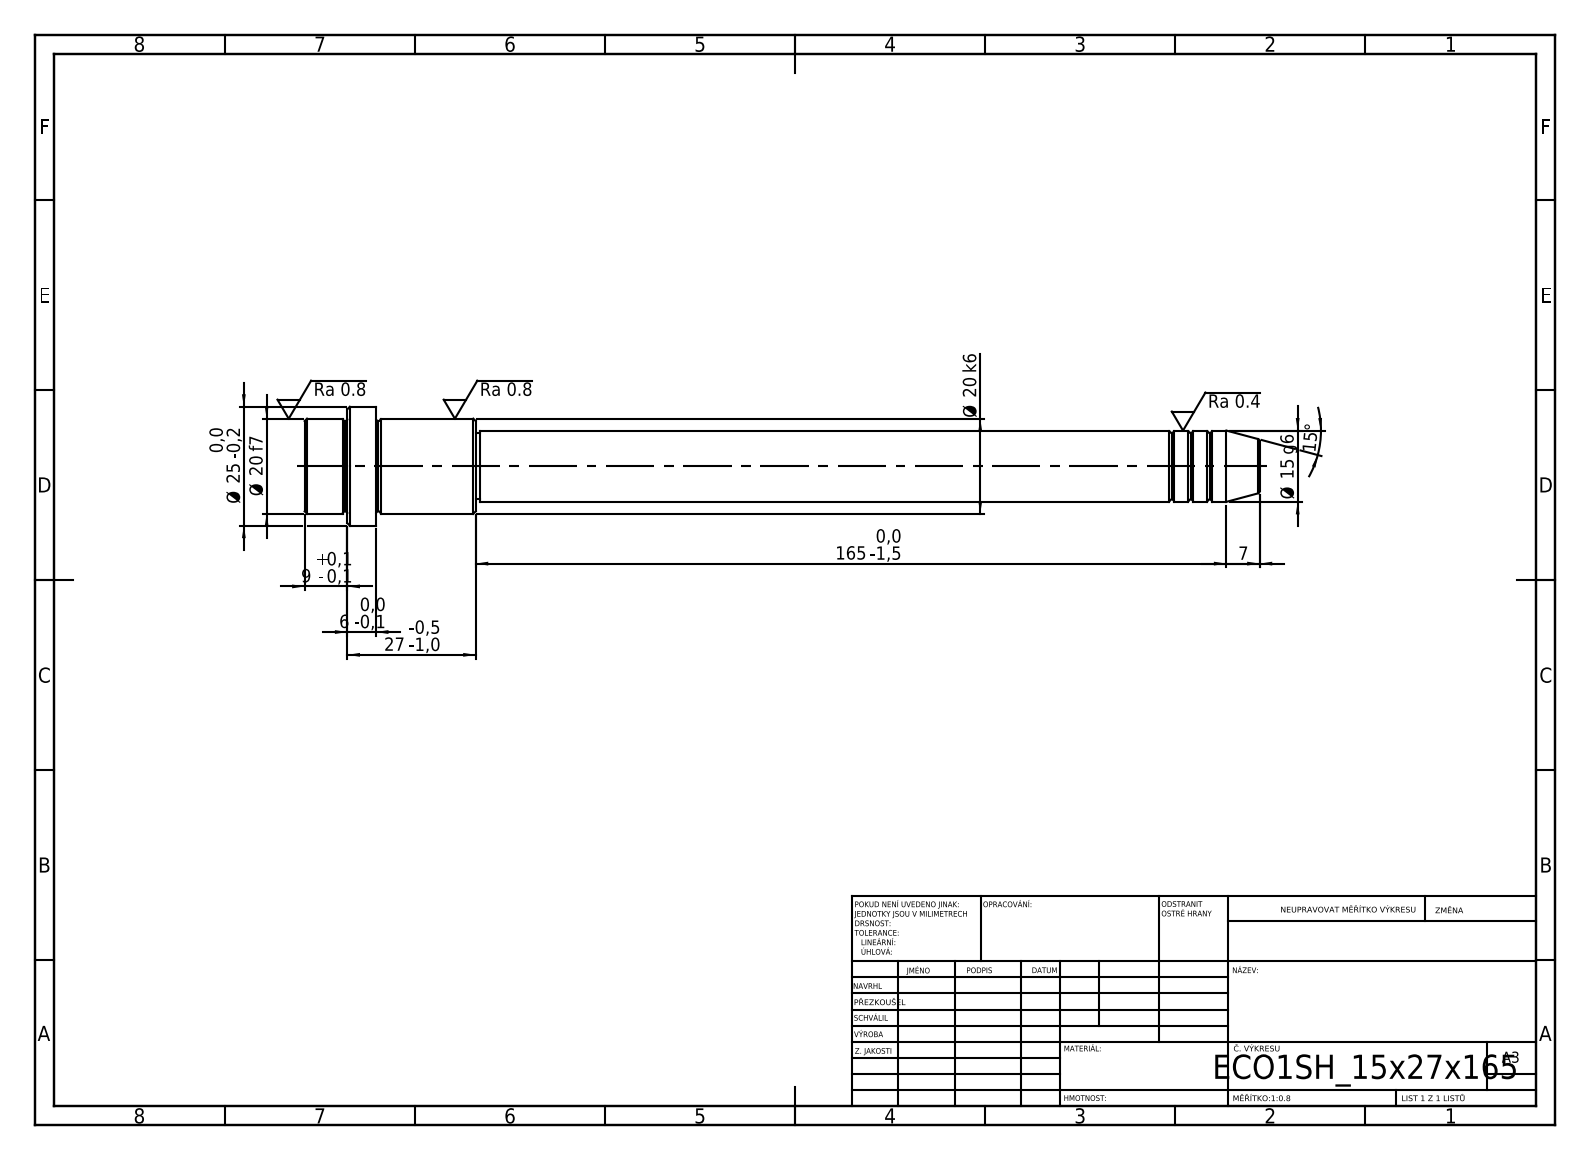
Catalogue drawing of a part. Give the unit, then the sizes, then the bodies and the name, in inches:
Units: inches
Overall size (bounding box): 7.913 × 0.984 × 0.984
Round bosses / shafts (diameter × count): ⌀0.984 ×1, ⌀0.787 ×1, ⌀0.591 ×1, ⌀0.551 ×1
Main face-to-face distances: 0.591, 0.236, 0.354, 0.827, 1.063, 1.417, 6.496, 7.323, 7.559, 7.913
Volume: 2.508 in³ · Surface area: 17.23 in²
Bodies: 1 solid, 52 faces (6 planar, 16 cylindrical, 30 other)
STEP written by: SolidWorks 2019 (CONFIG_CONTROL_DESIGN)
